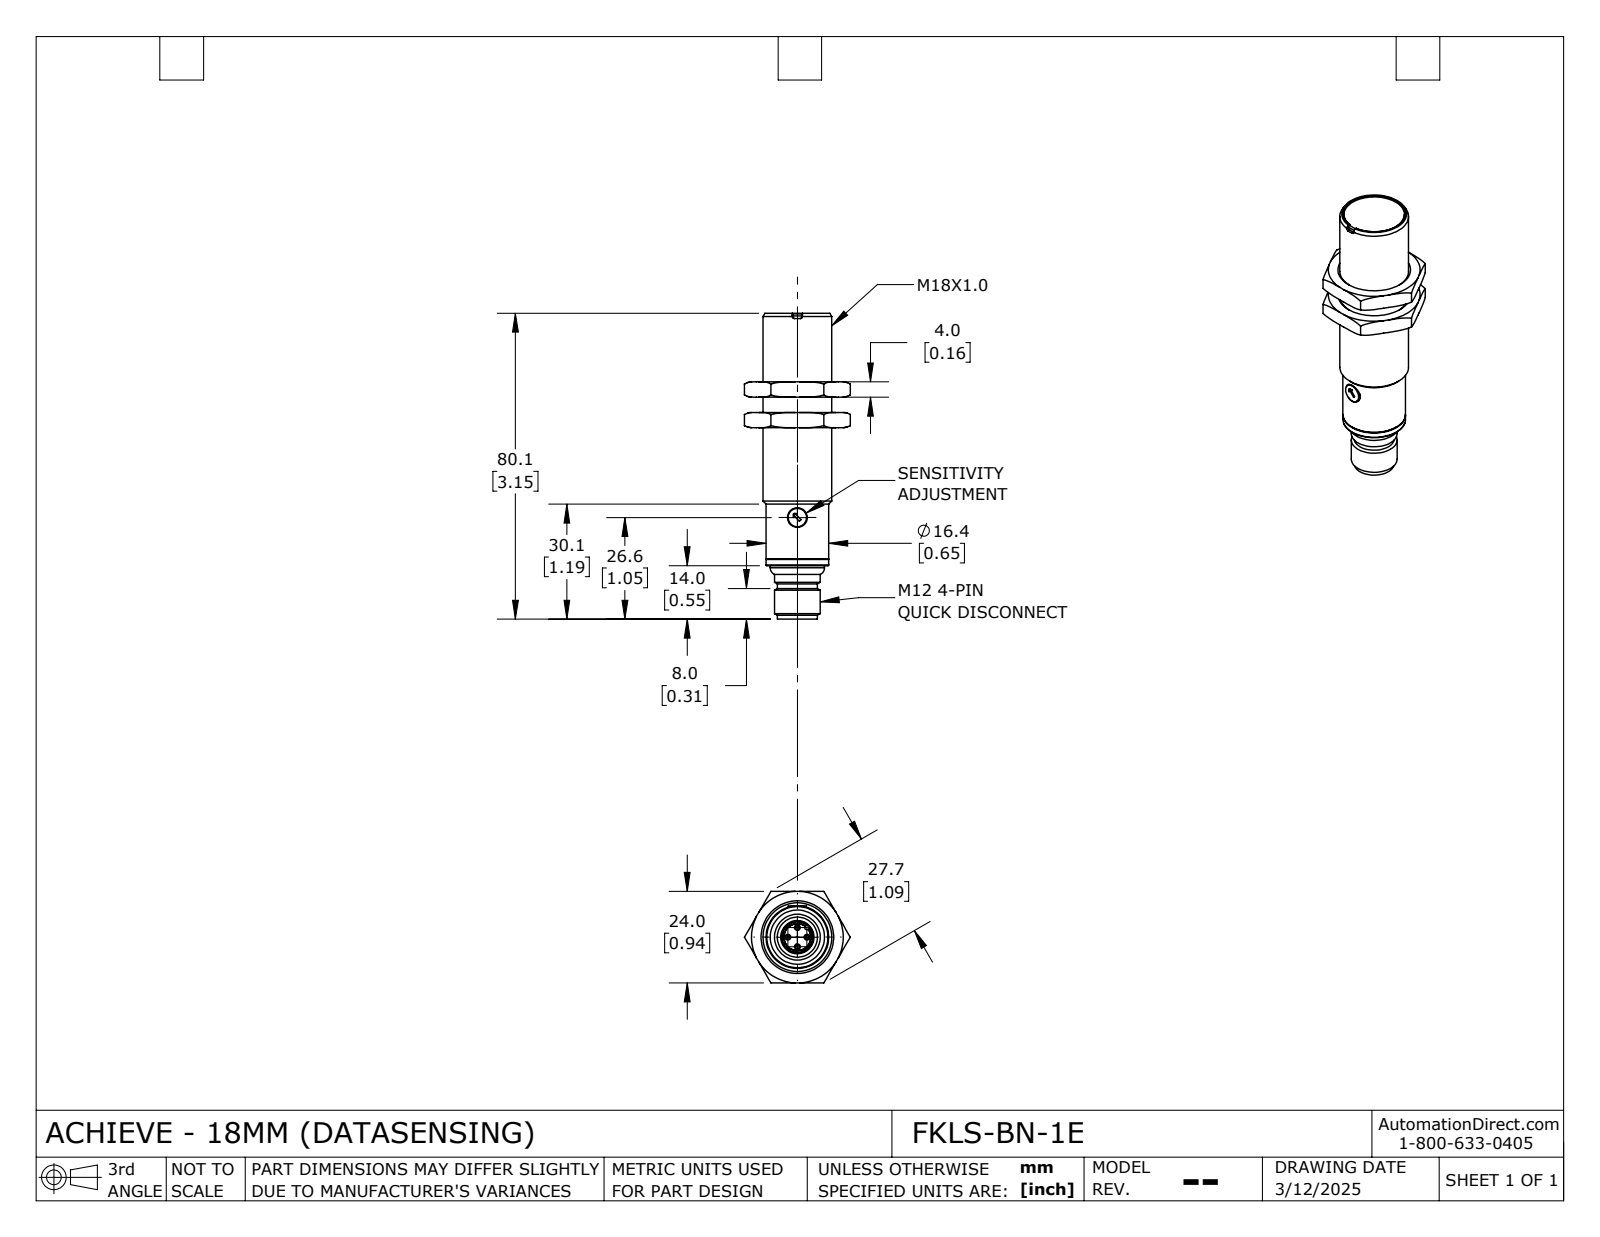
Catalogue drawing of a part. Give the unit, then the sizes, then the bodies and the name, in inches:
Units: inches
Overall size (bounding box): 3.154 × 1.091 × 0.945
Round holes (diameter × count): ⌀0.106 ×1, ⌀0.185 ×1, ⌀0.278 ×1, ⌀0.327 ×1, ⌀0.622 ×1, ⌀0.709 ×1
Round bosses / shafts (diameter × count): ⌀0.039 ×4, ⌀0.646 ×1, ⌀0.559 ×1, ⌀0.472 ×1, ⌀0.413 ×1, ⌀0.276 ×1, ⌀0.189 ×1
Partial cylindrical surfaces — rounded edges, fillets, slot ends (radius × count): R0.02 ×4, R0.024 ×1, R0.331 ×1
Main face-to-face distances: 0.157, 0.315, 0.945, 0.472, 0.055, 0.348, 0.403, 0.612, 0.96, 1.015
Volume: 1.259 in³ · Surface area: 12.98 in²
Bodies: 4 solids, 135 faces (54 planar, 29 cylindrical, 52 other)
Part name (STEP PRODUCT): FKLS-BN-1E_Default
STEP written by: SolidWorks 2024 (CONFIG_CONTROL_DESIGN)
